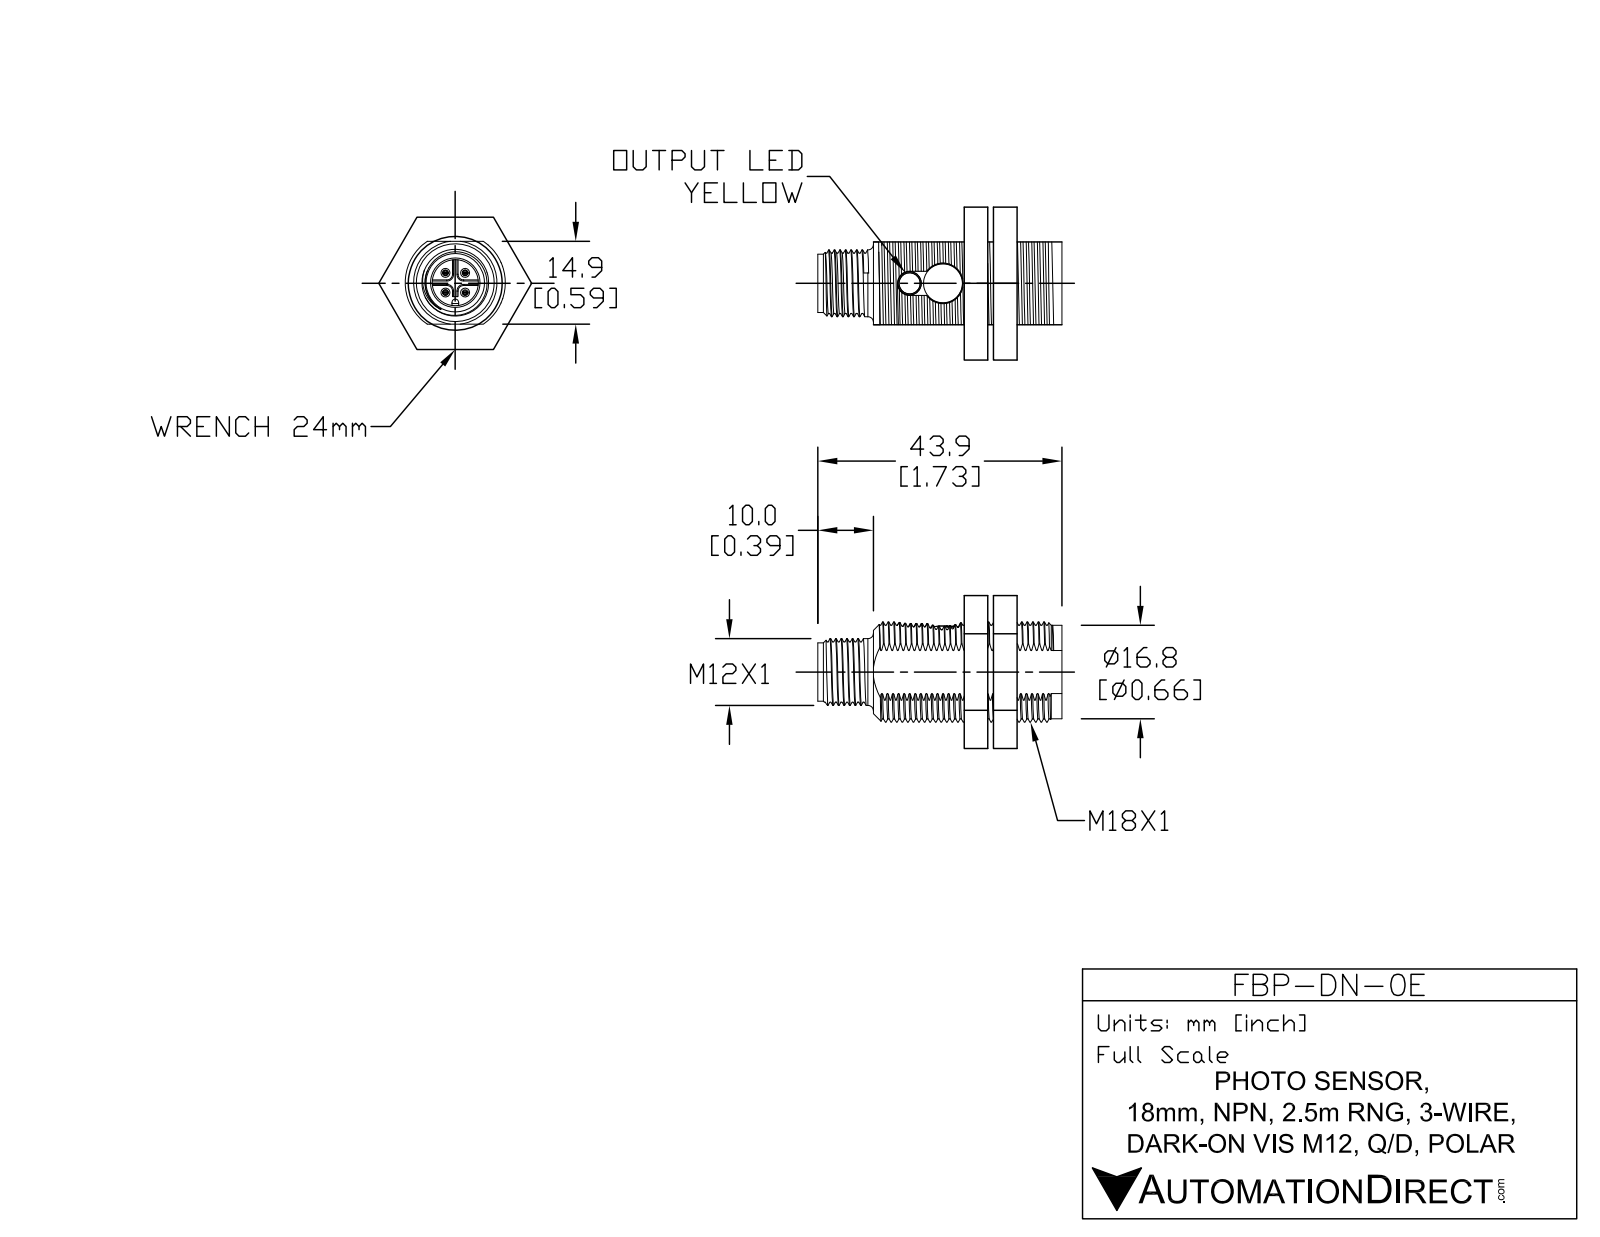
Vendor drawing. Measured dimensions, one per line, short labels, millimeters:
name: FBP-DN-0E
written by: SolidWorks 2011 (AUTOMOTIVE_DESIGN)
unit: mm
bodies: 7 solids, 217 faces (129 planar, 30 cylindrical, 58 other)
size: 43.9 × 27.69 × 24.57
volume: 10 286 mm³; area: 5 154 mm²
holes: 1× ⌀2.36, 1× ⌀4.26, 1× ⌀7.25, 1× ⌀8.4
bosses: 4× ⌀1, 1× ⌀12, 1× ⌀10.4
rounds: 2× R6.46, 2× R7.46, 1× R0.5, 1× R8.4, 1× R8.5, 1× R9
face distances: 8, 4.5, 24, 15, 1, 12.5, 4.9, 3.5, 12.9, 13.9
hole spacings: 6.61
